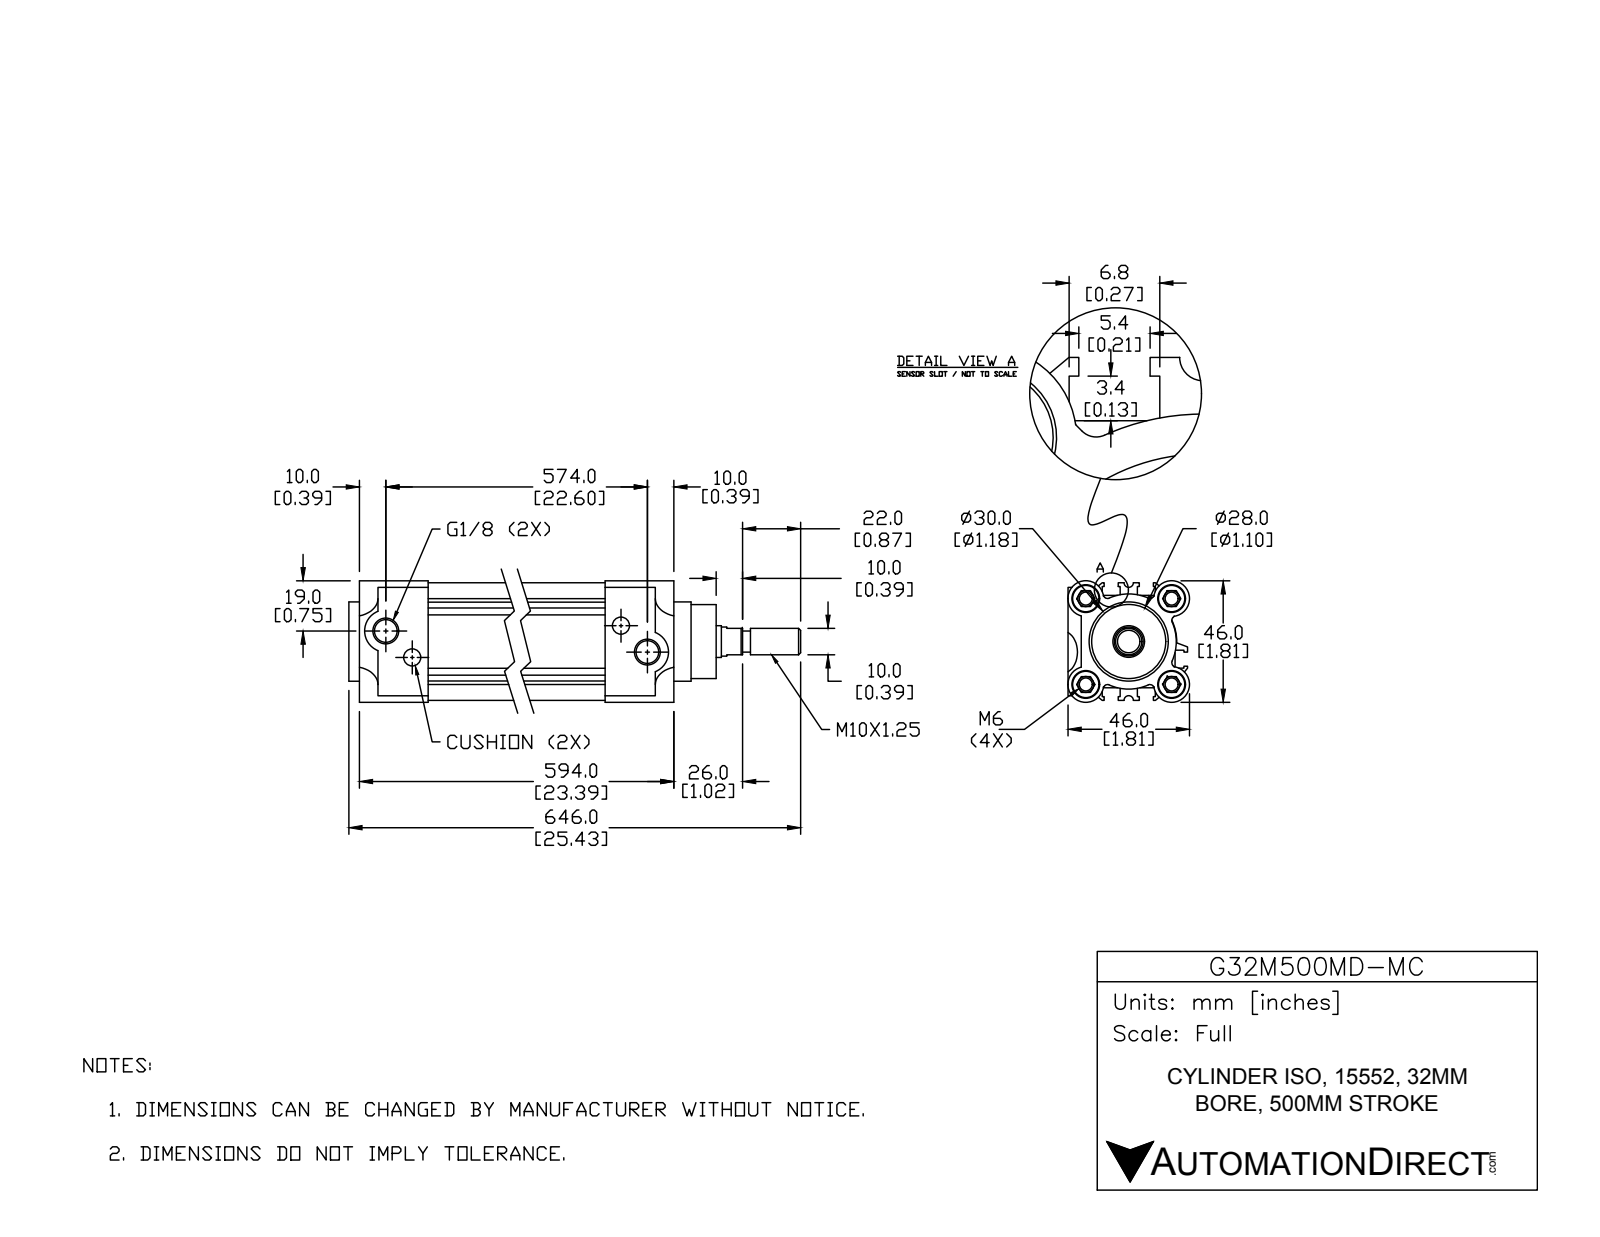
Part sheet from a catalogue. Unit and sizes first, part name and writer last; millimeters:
Units: millimetres
Overall size (bounding box): 646 × 46 × 46
Round holes (diameter × count): ⌀4.9 ×4, ⌀10.5 ×4, ⌀6.5 ×2, ⌀8.6 ×2, ⌀12 ×1
Round bosses / shafts (diameter × count): ⌀10 ×5, ⌀32 ×1, ⌀30 ×1, ⌀28 ×1, ⌀11 ×1, ⌀8 ×1
Partial cylindrical surfaces — rounded edges, fillets, slot ends (radius × count): R0.1 ×12, R1.5 ×6, R6 ×4, R6.8 ×4, R1.8 ×2, R8 ×2, R18 ×1, R18.2 ×1
Main face-to-face distances: 39.8, 4.7, 6.8, 25.5, 19, 12.2, 32.3, 35, 44.5, 13.3
Hole centre spacings: 23, 32.5, 14.1, 45.9, 564, 554.1, 574.1
Volume: 665 300 mm³ · Surface area: 253 400 mm²
Bodies: 4 solids, 411 faces (229 planar, 138 cylindrical, 44 other)
Part name (STEP PRODUCT): G32M500MD-MC; 32121500-R; 32121-HR; 32-500-73.5-B (+1 more)
STEP written by: SolidWorks 2015 (CONFIG_CONTROL_DESIGN)
